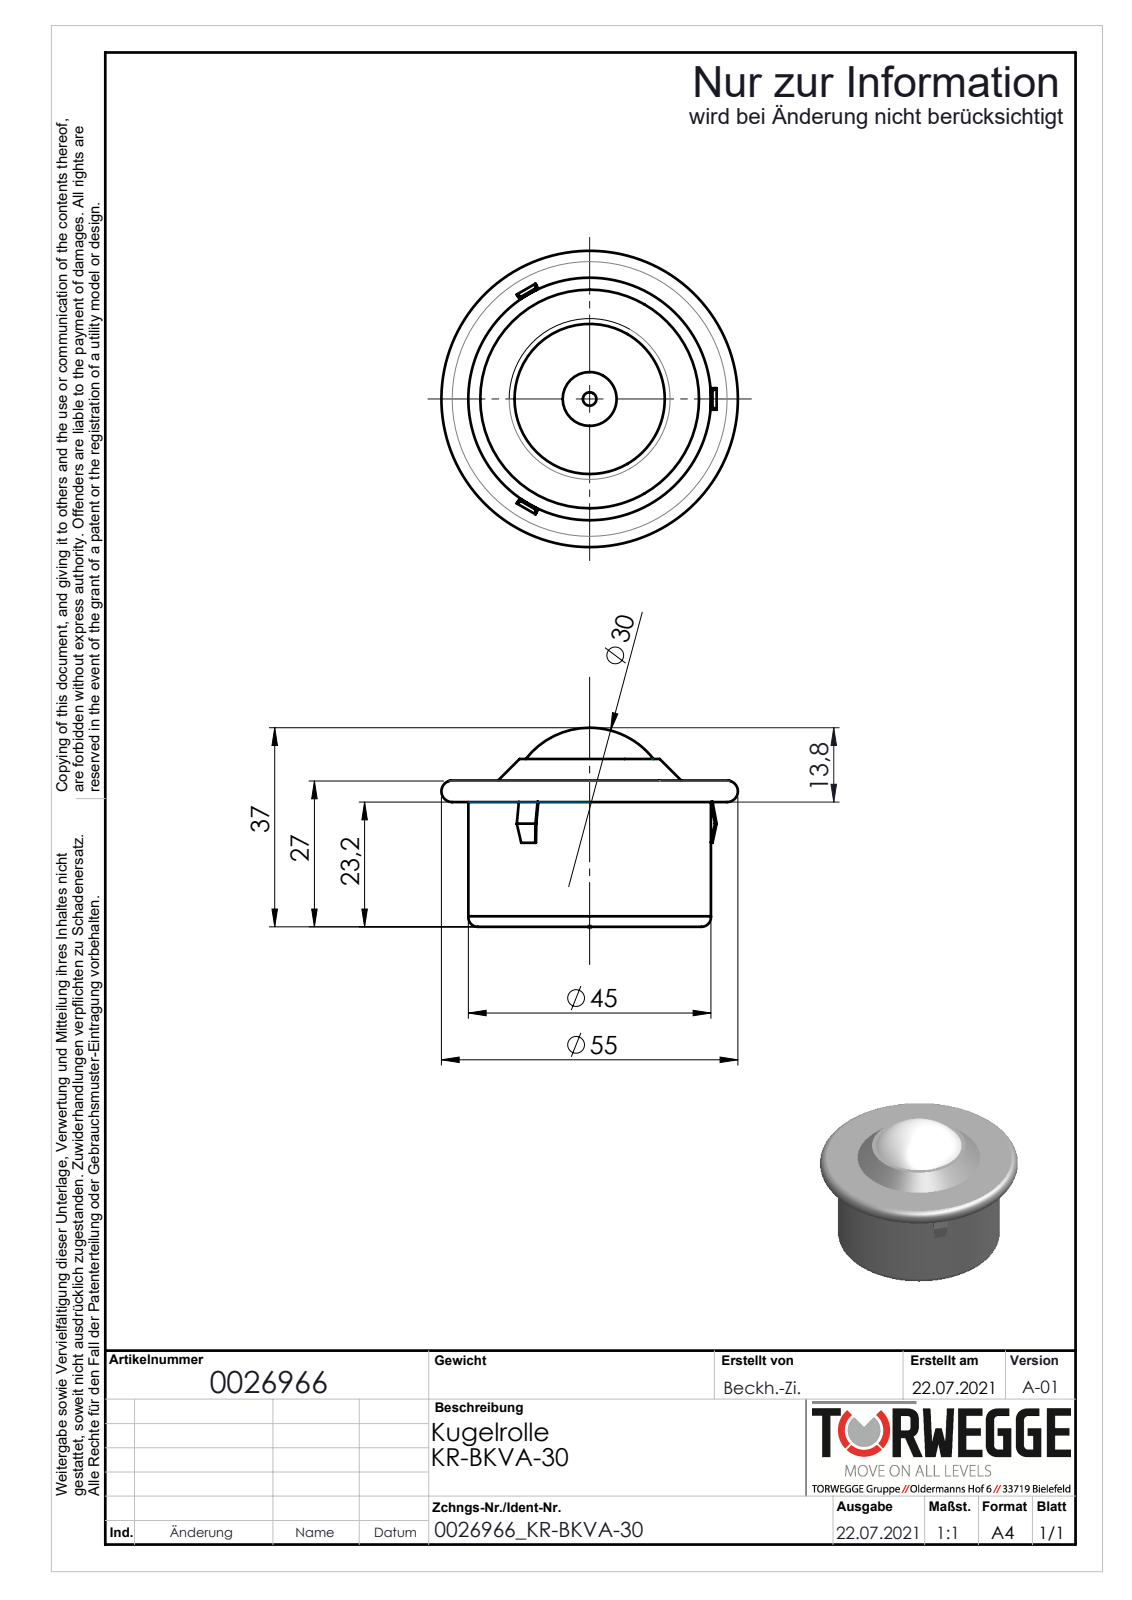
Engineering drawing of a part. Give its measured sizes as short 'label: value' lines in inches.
name: 0026966
written by: SolidWorks 2020 (AUTOMOTIVE_DESIGN)
unit: in
bodies: 0 solids, 73 faces (34 planar, 6 cylindrical, 33 other)
size: 2.165 × 2.165 × 1.455
holes: 1× ⌀0.098, 1× ⌀0.394
bosses: 1× ⌀1.772
face distances: 0.157, 0.315
